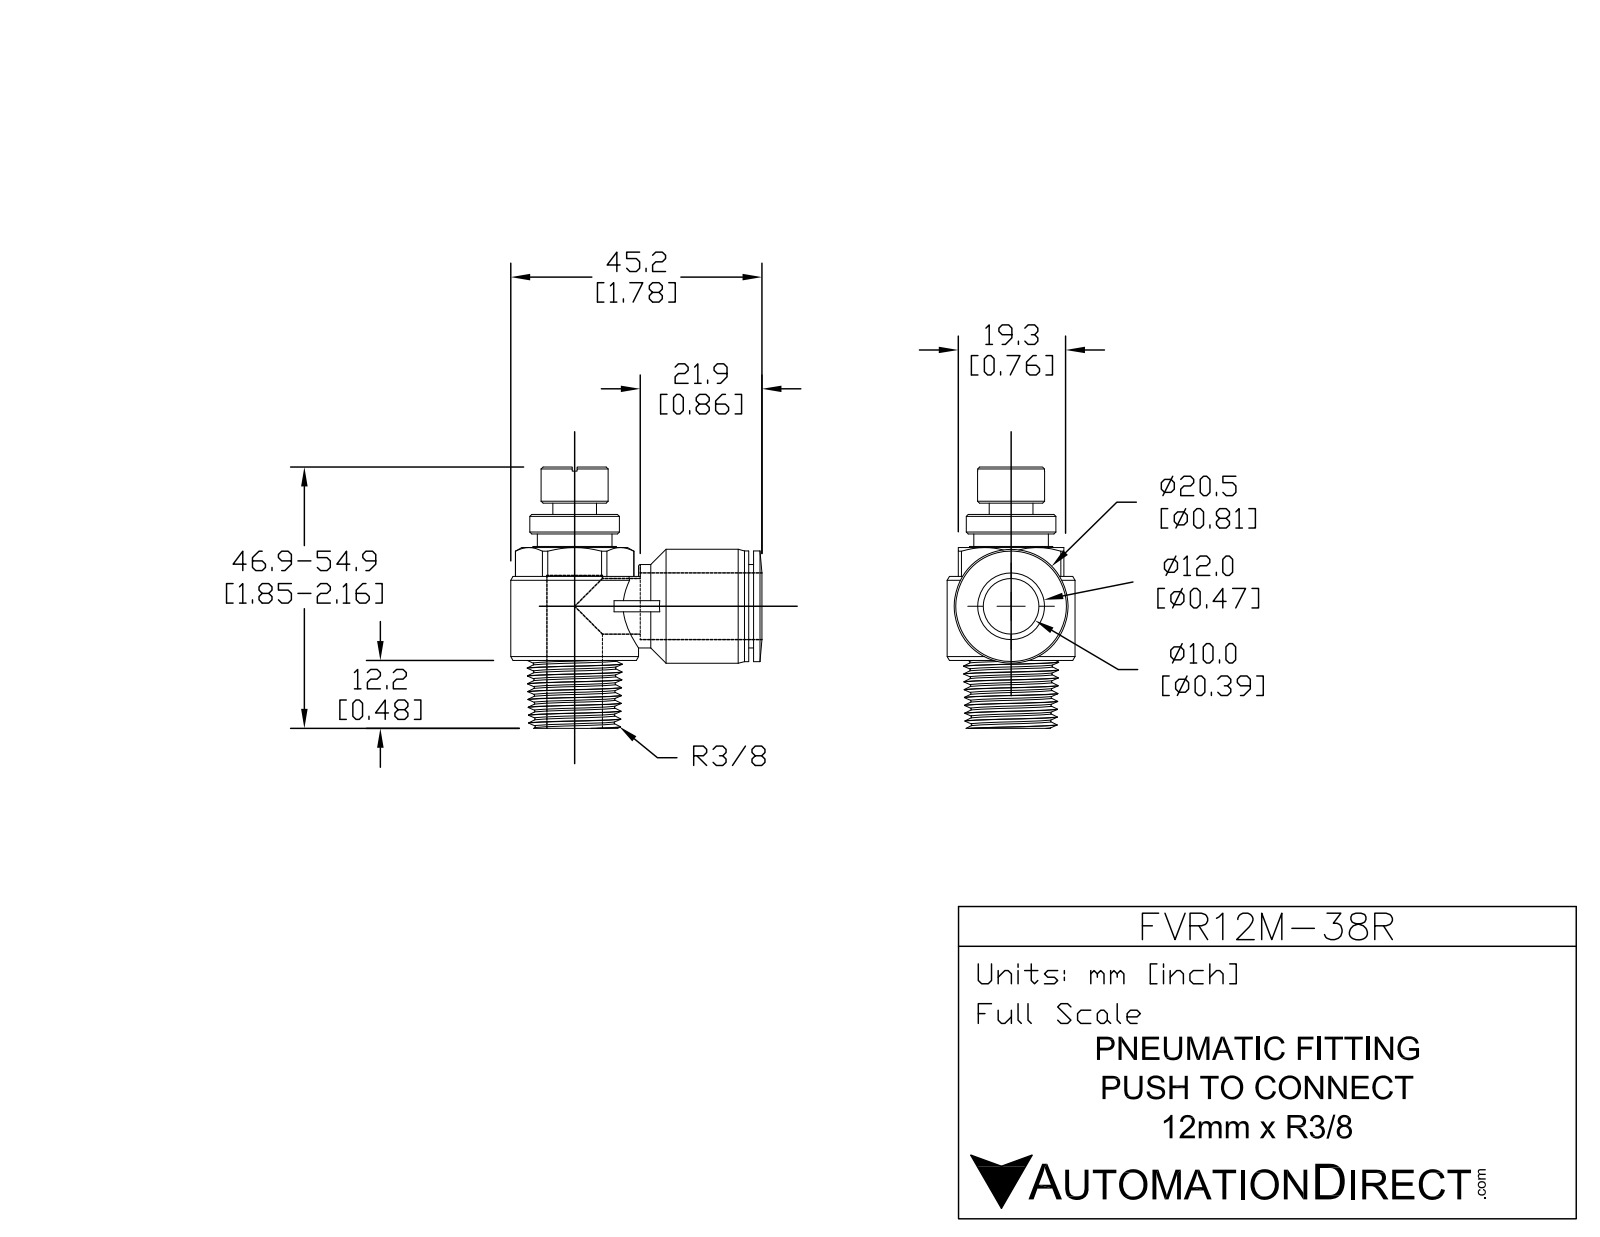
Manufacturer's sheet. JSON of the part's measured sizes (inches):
{"part_name": "FVR12M-38R", "step_written_by": "SolidWorks 2015 (AUTOMOTIVE_DESIGN)", "units": "inches", "bodies": {"solids": 1, "faces": 567, "planar": 255, "cylindrical": 144, "other": 168}, "overall_size": [2.236, 1.778, 0.906], "volume_in3": 1.012, "surface_area_in2": 11.11, "round_holes": [[0.169, 2], [0.484, 1]], "round_bosses_or_shafts": [[0.748, 2], [0.591, 2], [0.906, 1], [0.807, 1], [0.787, 1], [0.675, 1], [0.673, 1], [0.547, 1]], "partial_cylinders_radius": [[0.236, 1], [0.315, 1], [0.413, 1]], "face_to_face_distances": [0.047, 1.035, 0.748, 0.807, 0.228, 0.559, 1.366, 1.594, 0.719, 0.766]}
